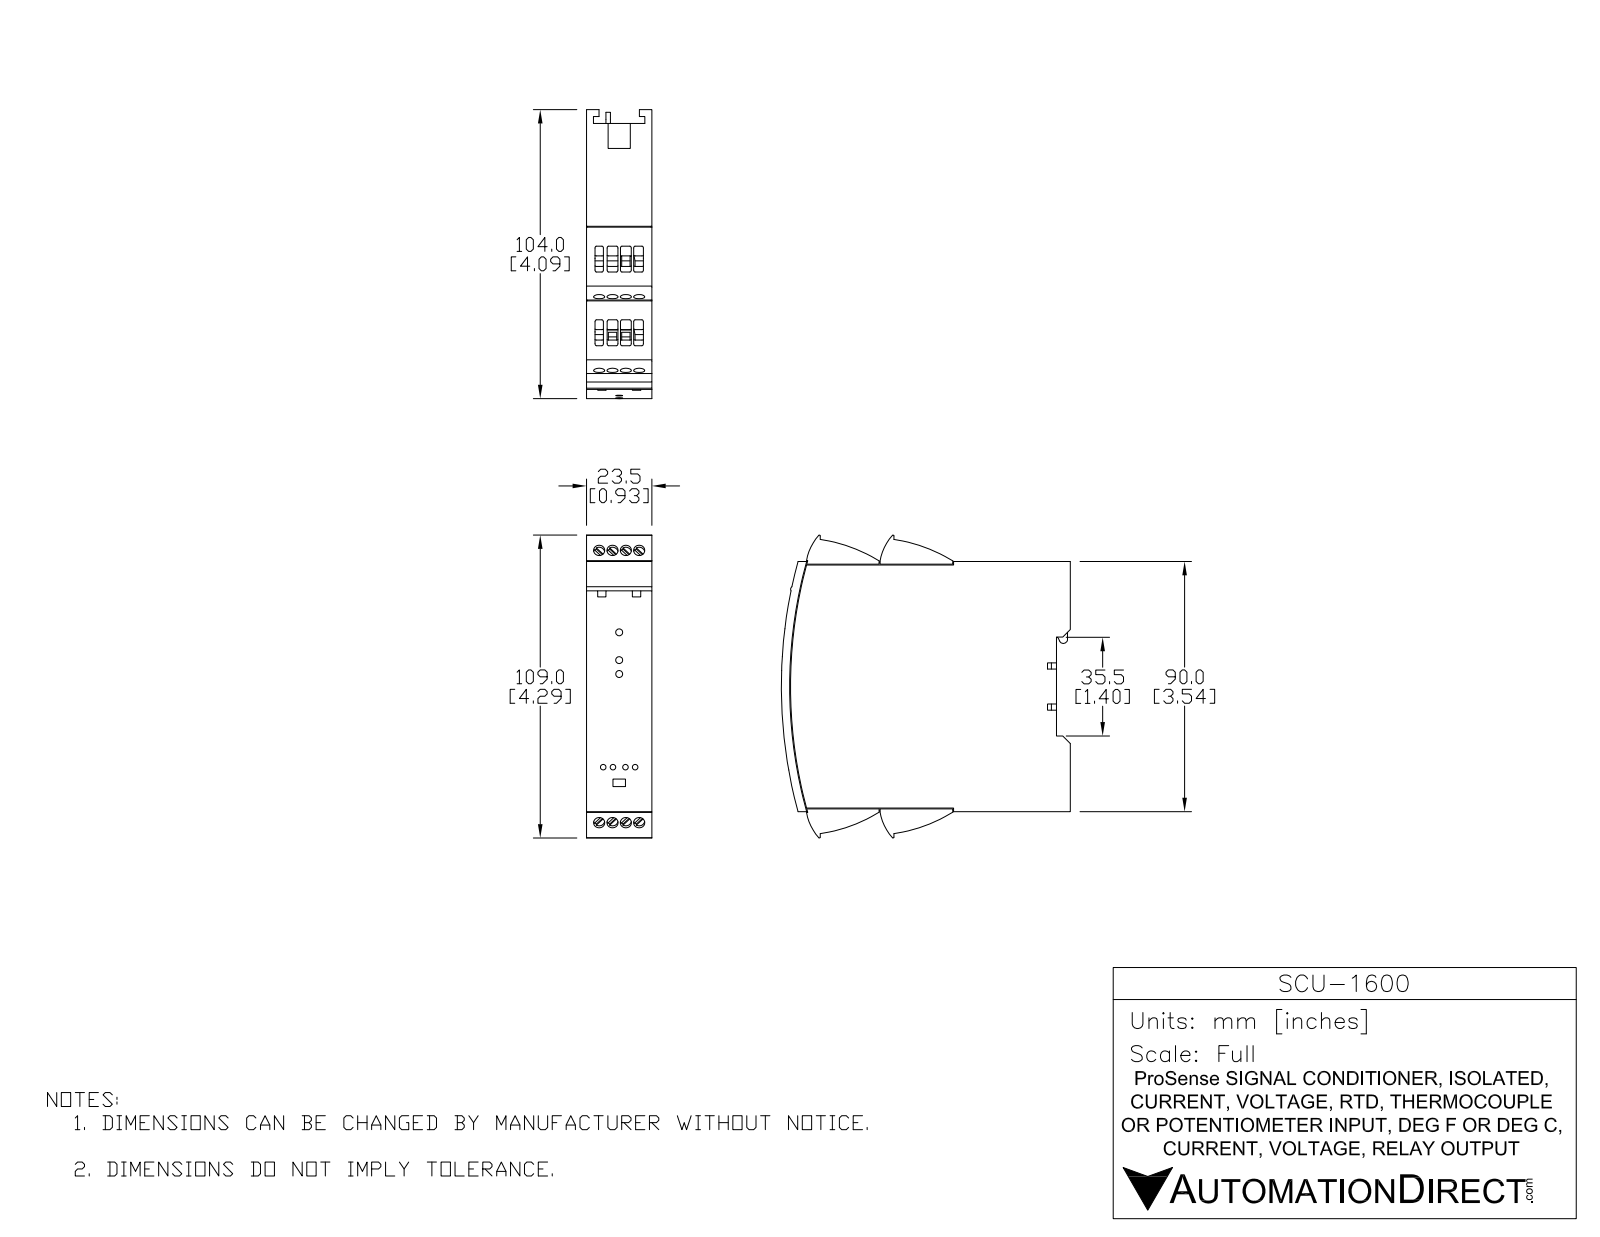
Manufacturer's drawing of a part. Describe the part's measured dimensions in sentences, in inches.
The part is named "SCU-1600". Its 3-D file was written by "SolidWorks 2017 (AUTOMOTIVE_DESIGN)". It is 1 solid with 1027 faces: 618 planar, 201 cylindrical and 208 other. Overall it measures 4.291 by 4.094 by 0.925 inches. Its volume is 13.23 cubic inches and its surface area 50.78 square inches. Round holes: 16 of diameter 0.157, 4 of diameter 0.079, 4 of diameter 0.091, 2 of diameter 0.098. Partial cylindrical surfaces (rounded edges, fillets, slot ends): 67 of radius 0.02, 4 of radius 0.012, 4 of radius 0.726, 4 of radius 2.175, 3 of radius 6.762, 2 of radius 0.039, 1 of radius 0.043, 1 of radius 0.059. The main face-to-face distances are 0.925, 3.543, 0.098, 0.197, 0.189, 0.177, 0.65, 0.12, 0.805, 0.157. The hole center spacings are 0.189, 0.434, 0.378, 0.391, 0.544, 0.567, 0.689, 0.138.
